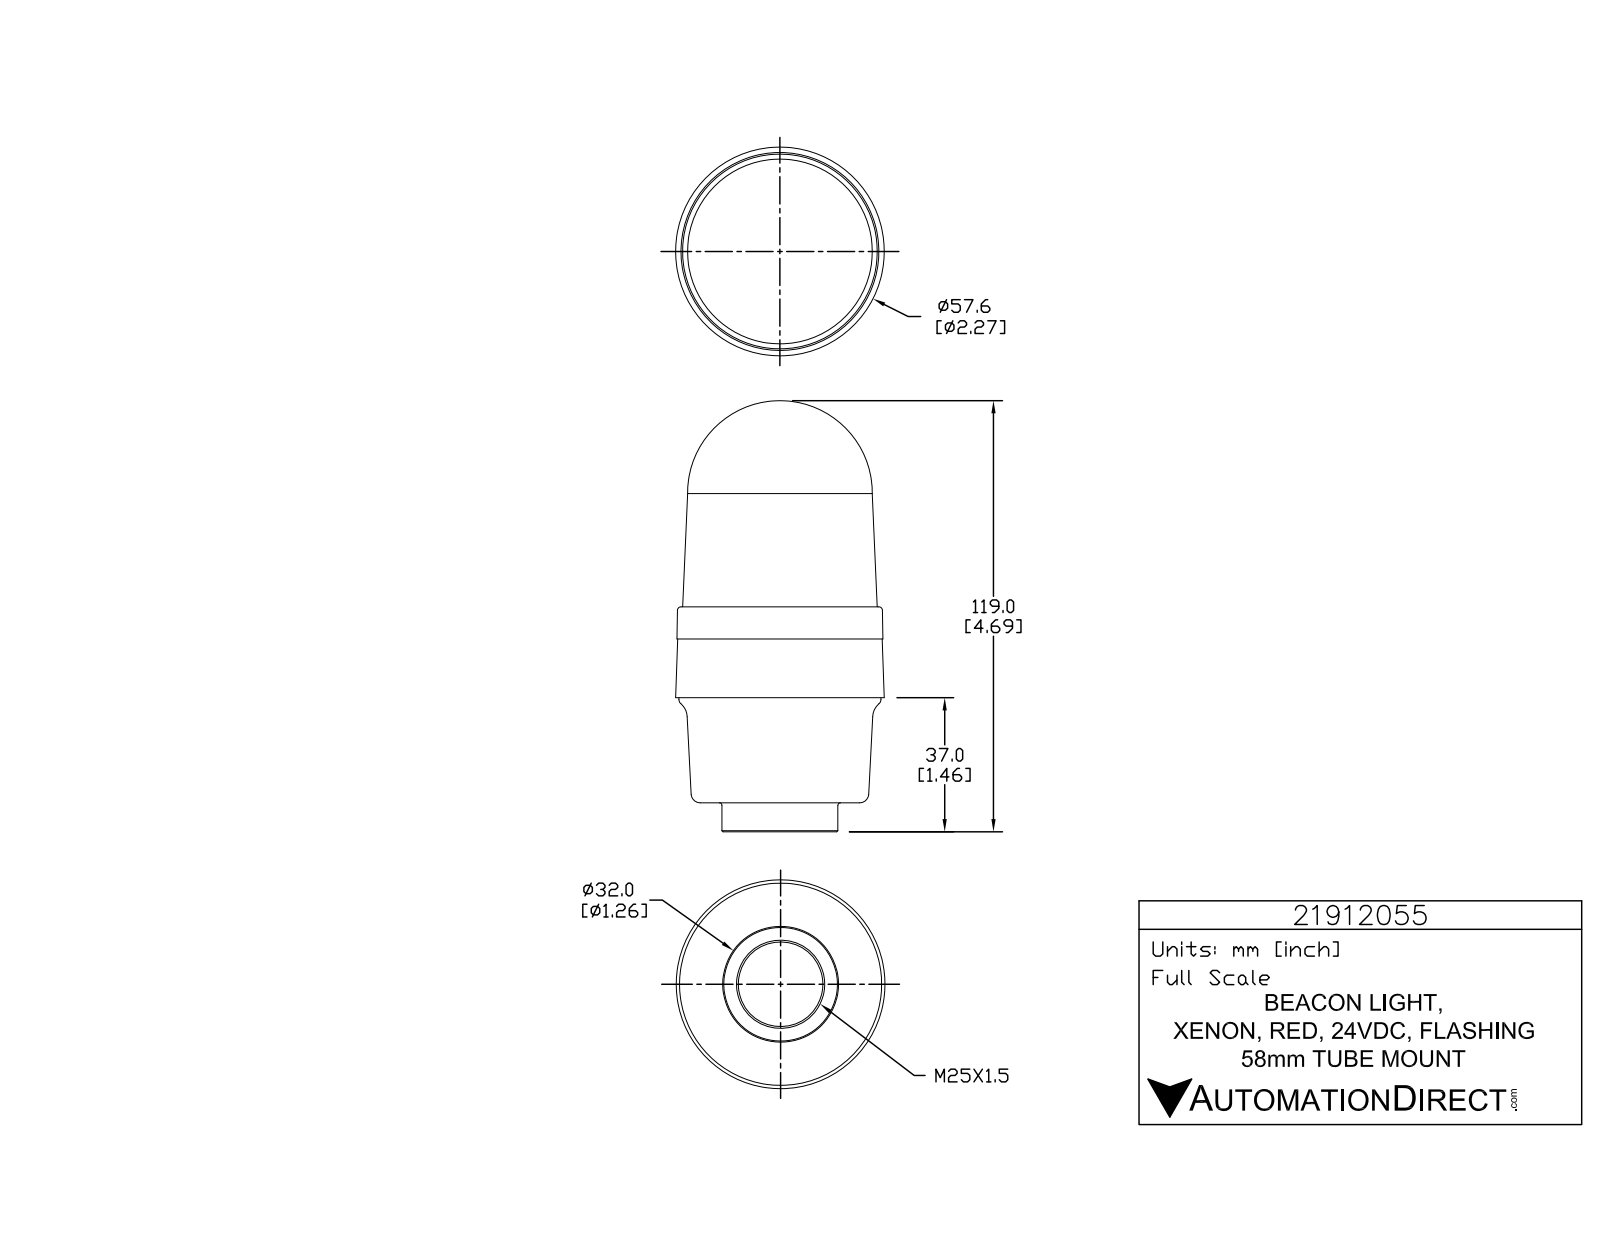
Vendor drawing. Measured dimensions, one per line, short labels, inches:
name: 21912055
written by: SolidWorks 2015 (AUTOMOTIVE_DESIGN)
unit: in
bodies: 1 solid, 791 faces (525 planar, 168 cylindrical, 98 other)
size: 4.685 × 2.269 × 2.269
volume: 13.89 in³; area: 34.06 in²
holes: 3× ⌀0.039, 1× ⌀0.92
bosses: 3× ⌀0.226, 3× ⌀0.056, 1× ⌀2.197, 1× ⌀1.26
rounds: 6× R0.008, 6× R0.008, 6× R0.008, 6× R0.131, 3× R0.004, 3× R0.005, 3× R0.008, 3× R0.008
face distances: 0.315, 1.142, 1.457, 0.988, 2.13, 2.445, 0.35, 0.638, 1.78, 2.094
